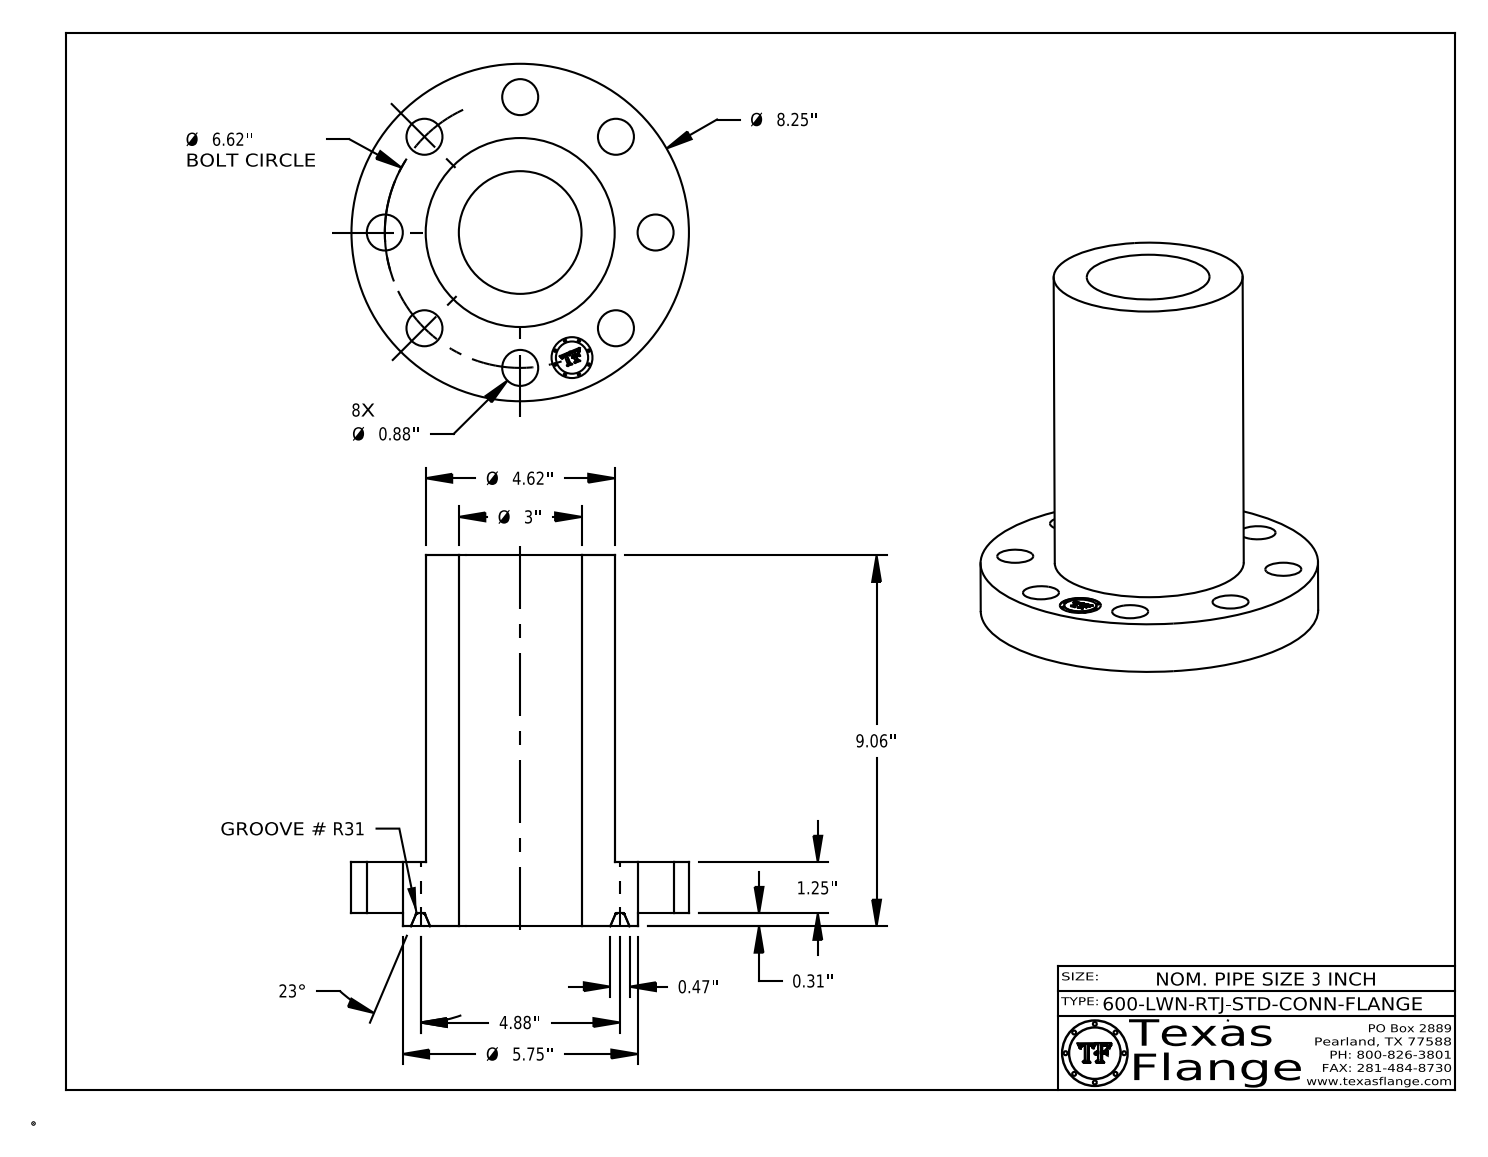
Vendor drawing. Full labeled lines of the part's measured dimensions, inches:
Part name (STEP PRODUCT): 3-600-LWN-RTJ-STD-CONN-FLANGE
STEP written by: CATIA V5 STEP AP214 (AUTOMOTIVE_DESIGN)
Units: inches
Bodies: 1 solid, 431 faces (371 planar, 52 cylindrical, 8 other)
Overall size (bounding box): 9.063 × 8.25 × 8.25
Volume: 128.9 in³ · Surface area: 349.3 in²
Round holes (diameter × count): ⌀0.88 ×8, ⌀1 ×1, ⌀3 ×1
Round bosses / shafts (diameter × count): ⌀0.061 ×8, ⌀8.25 ×1, ⌀5.75 ×1, ⌀4.62 ×1, ⌀0.788 ×1
Main face-to-face distances: 1.25, 0.313, 1.563, 9.063, 8.75, 7.5, 1.558, 1.245, 7.505, 0.298
Hole centre spacings: 3.31, 2.533, 6.116, 4.681, 4.681, 1.291, 3.678, 6.493
